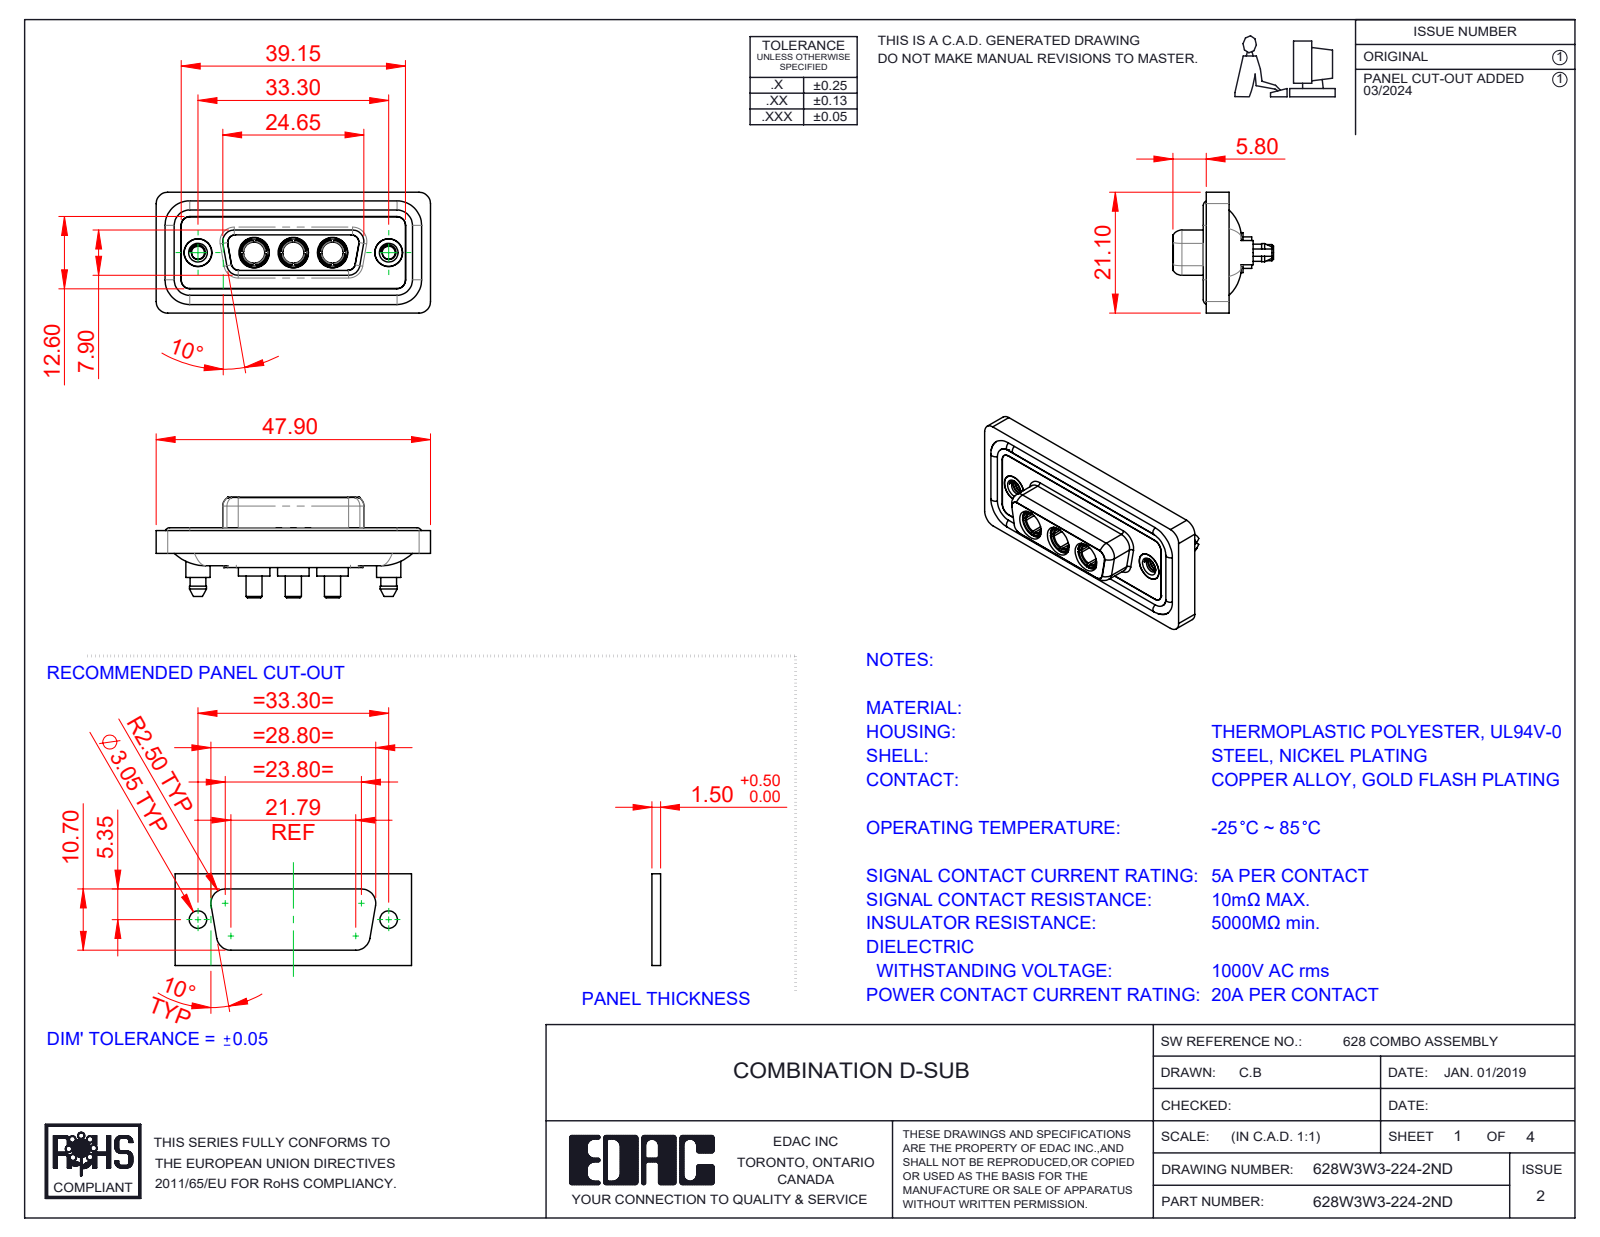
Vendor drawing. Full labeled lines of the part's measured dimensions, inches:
Part name (STEP PRODUCT): 628Combo Housing_3W3; 628Combo Waterproof Housing_15 Contacts; 628Combo Threaded Boardlock_D; 628W3W3-224-2ND (+3 more)
STEP written by: SolidWorks 2023 (CONFIG_CONTROL_DESIGN)
Units: inches
Bodies: 13 solids, 674 faces (208 planar, 305 cylindrical, 161 other)
Overall size (bounding box): 1.886 × 0.831 × 0.691
Volume: 0.376 in³ · Surface area: 15.62 in²
Round holes (diameter × count): ⌀0.191 ×5, ⌀0.146 ×3, ⌀0.209 ×3, ⌀0.089 ×2, ⌀0.157 ×2, ⌀0.159 ×2, ⌀0.197 ×2
Round bosses / shafts (diameter × count): ⌀0.063 ×4, ⌀0.217 ×3, ⌀0.205 ×3, ⌀0.195 ×3, ⌀0.187 ×3, ⌀0.148 ×3, ⌀0.11 ×3, ⌀0.213 ×2
Partial cylindrical surfaces — rounded edges, fillets, slot ends (radius × count): R0.059 ×24, R0.079 ×20, R0.053 ×12, R0.063 ×10, R0.01 ×4, R0.02 ×4, R0.024 ×4, R0.026 ×4
Main face-to-face distances: 0.016, 0.071, 0.063, 0.02, 0.293, 0.043, 0.114, 0.222, 0.278, 0.26
Hole centre spacings: 0.27, 0.386, 0.656, 0.925, 0.539, 1.311
